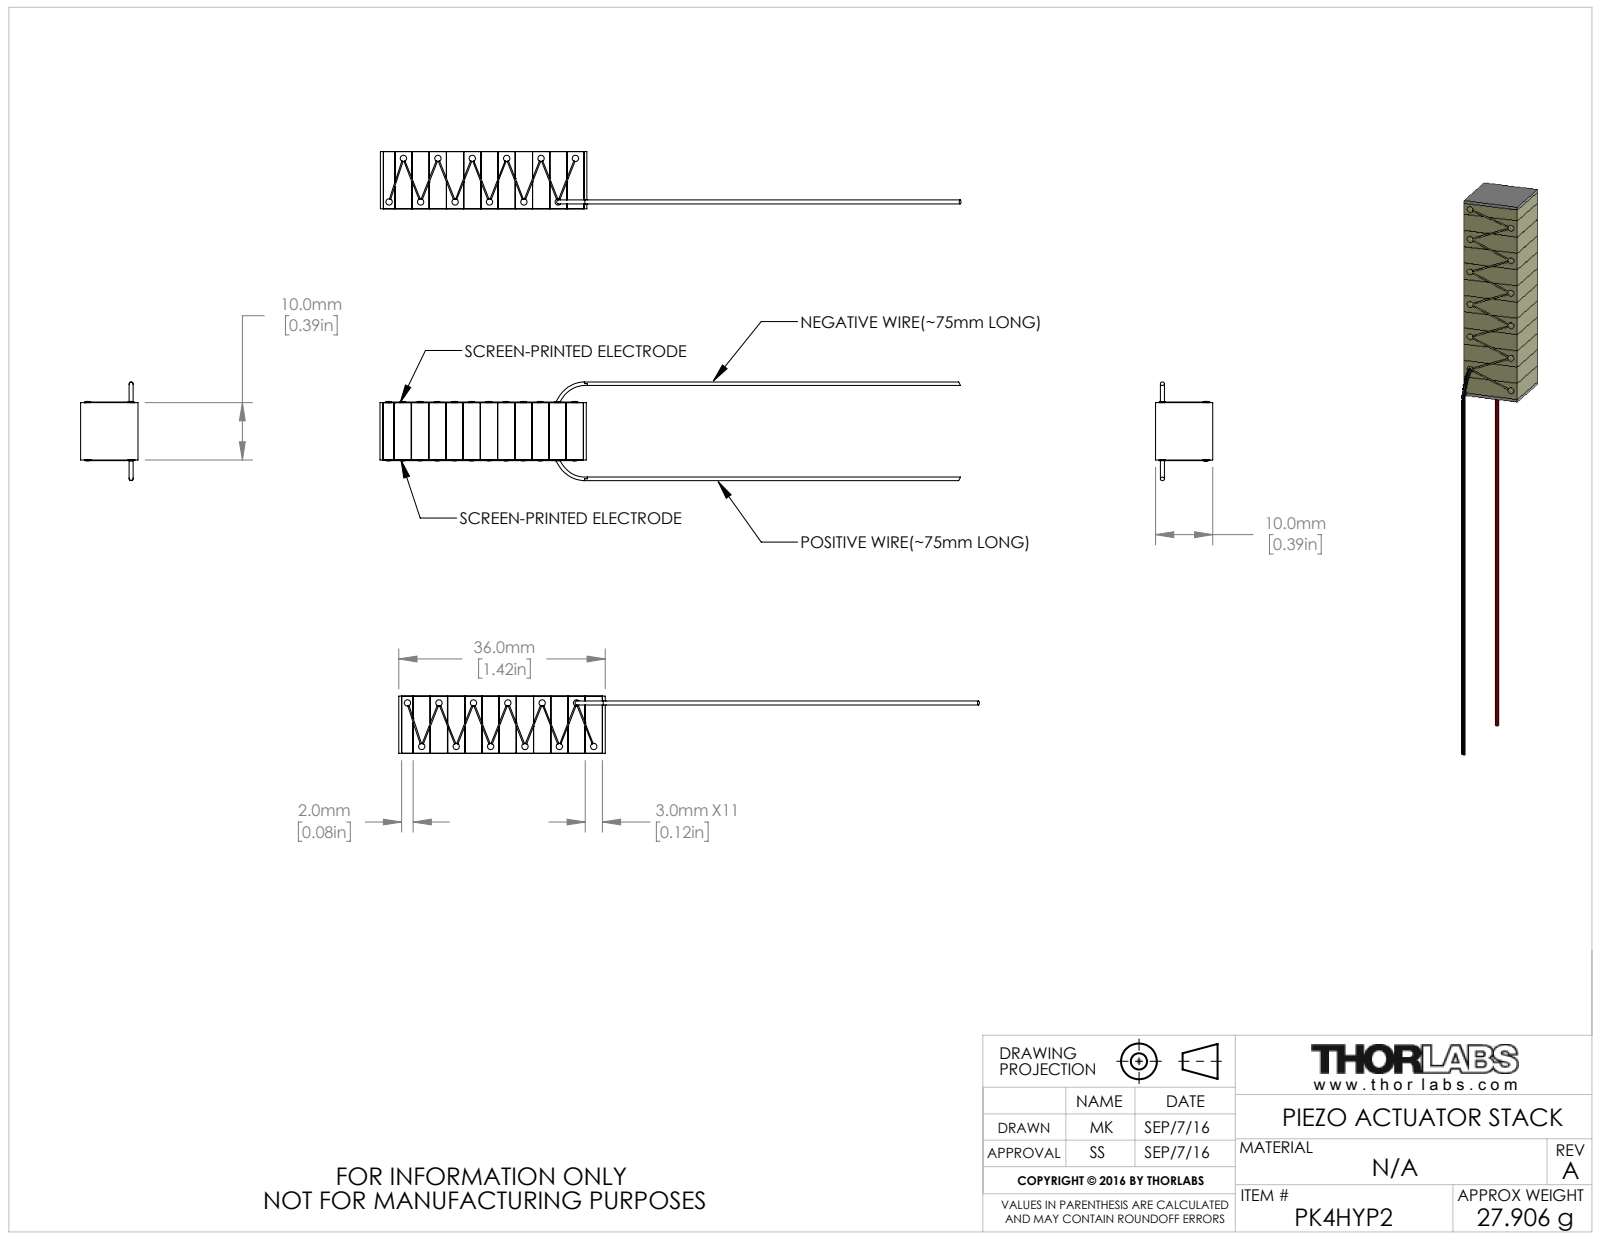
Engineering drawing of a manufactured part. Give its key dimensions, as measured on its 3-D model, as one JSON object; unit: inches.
{"part_name": "CTN003317", "step_written_by": "SolidWorks 2016 (AUTOMOTIVE_DESIGN)", "units": "inches", "bodies": {"solids": 4, "faces": 398, "planar": 226, "cylindrical": 72, "other": 100}, "overall_size": [3.991, 0.678, 0.394], "volume_in3": 0.437, "surface_area_in2": 13.02, "round_bosses_or_shafts": [[0.043, 12]], "face_to_face_distances": [0.118, 0.236, 0.119, 0.237, 0.394, 0.355, 0.473, 0.591, 0.709, 0.354]}
